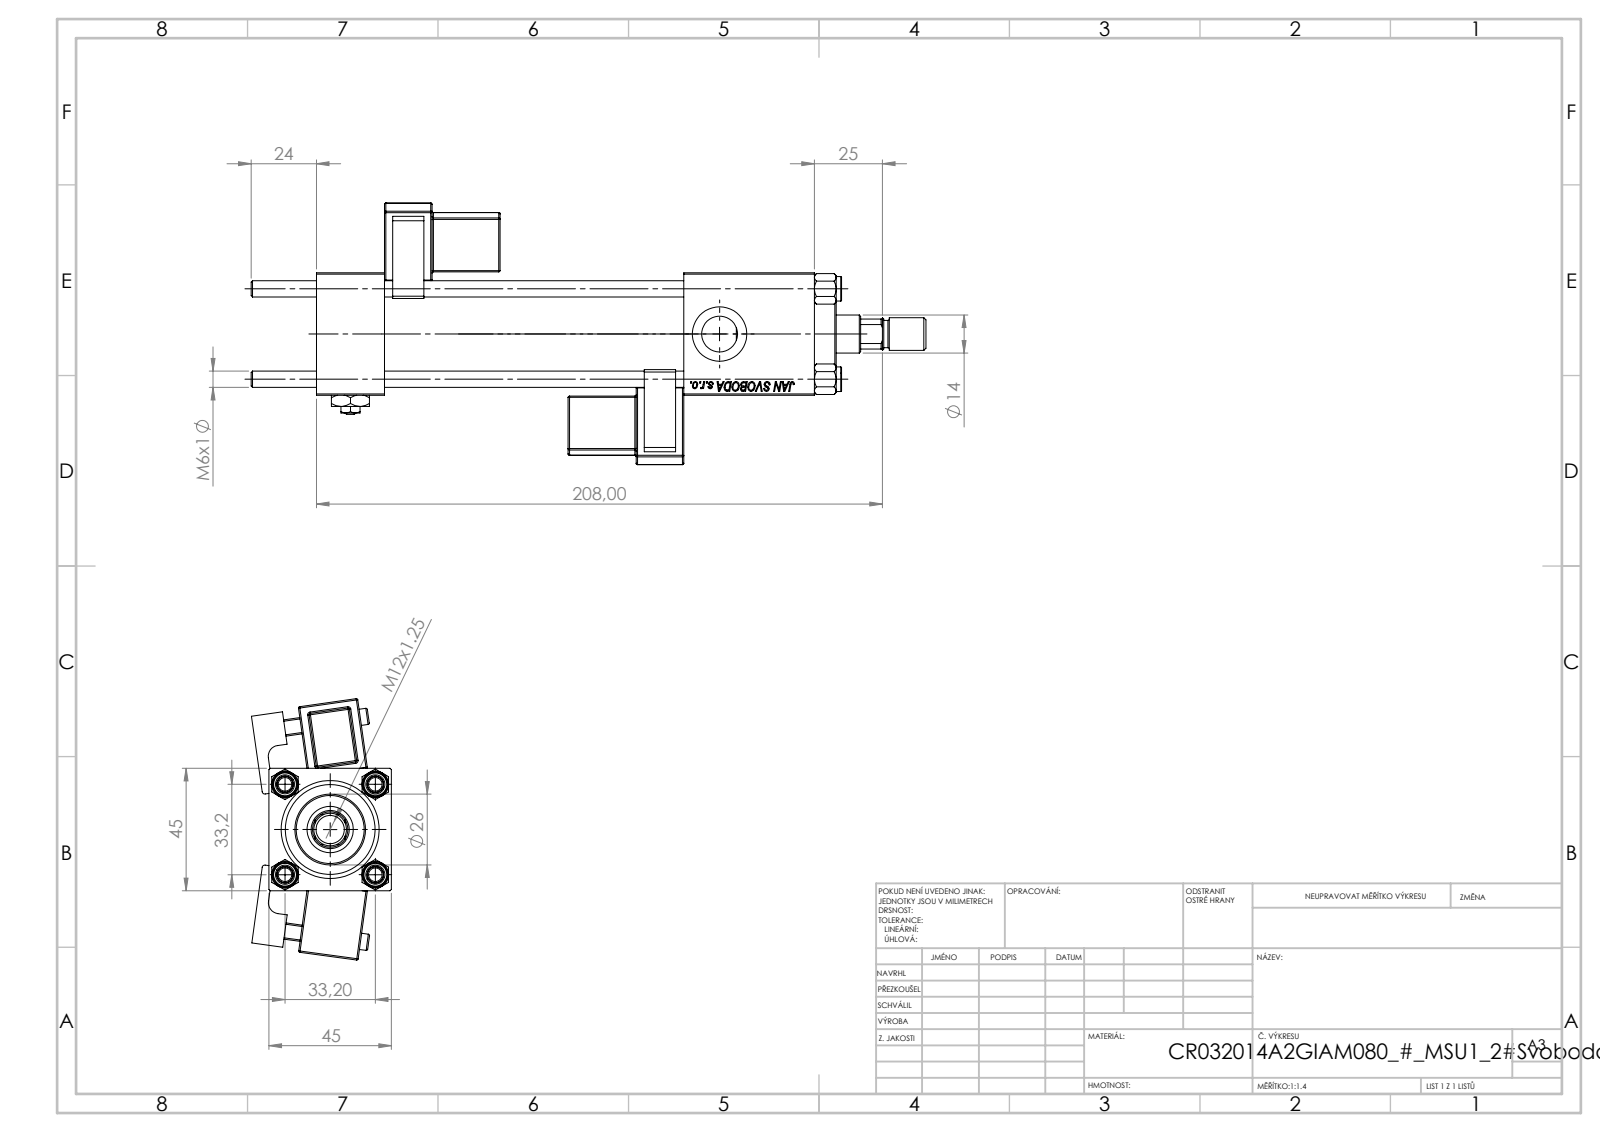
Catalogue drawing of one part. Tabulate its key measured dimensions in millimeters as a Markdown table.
| quantity | value |
| --- | --- |
| part name | ROD_END_AH; NUT_M5; V215CR_VCP; V215CR_MSU (+4 more) |
| STEP written by | SolidWorks 2019 (CONFIG_CONTROL_DESIGN) |
| units | millimeters |
| bodies | 15 solids, 1356 faces (608 planar, 148 cylindrical, 600 other) |
| overall size | 248 × 96.03 × 51.41 |
| volume | 275 663 mm³ |
| surface area | 107 101 mm² |
| round holes (diameter × count) | 6 × 4, 7 × 2, 13.16 × 2, 20 × 2, 6.5 × 1, 14 × 1, 17 × 1, 24 × 1, 32 × 1, 33 × 1 |
| round bosses / shafts (diameter × count) | 9 × 4, 6 × 2, 38 × 1, 26 × 1, 12 × 1, 10 × 1 |
| partial cylindrical surfaces (radius × count) | 0.5 × 48, 1 × 2, 2.5 × 2, 4 × 2, 6.5 × 1 |
| main face-to-face distances | 45, 25, 3, 135, 110, 183, 158, 48, 15, 92.5 |
| hole center spacings | 23.48, 33.2, 46.95 |
